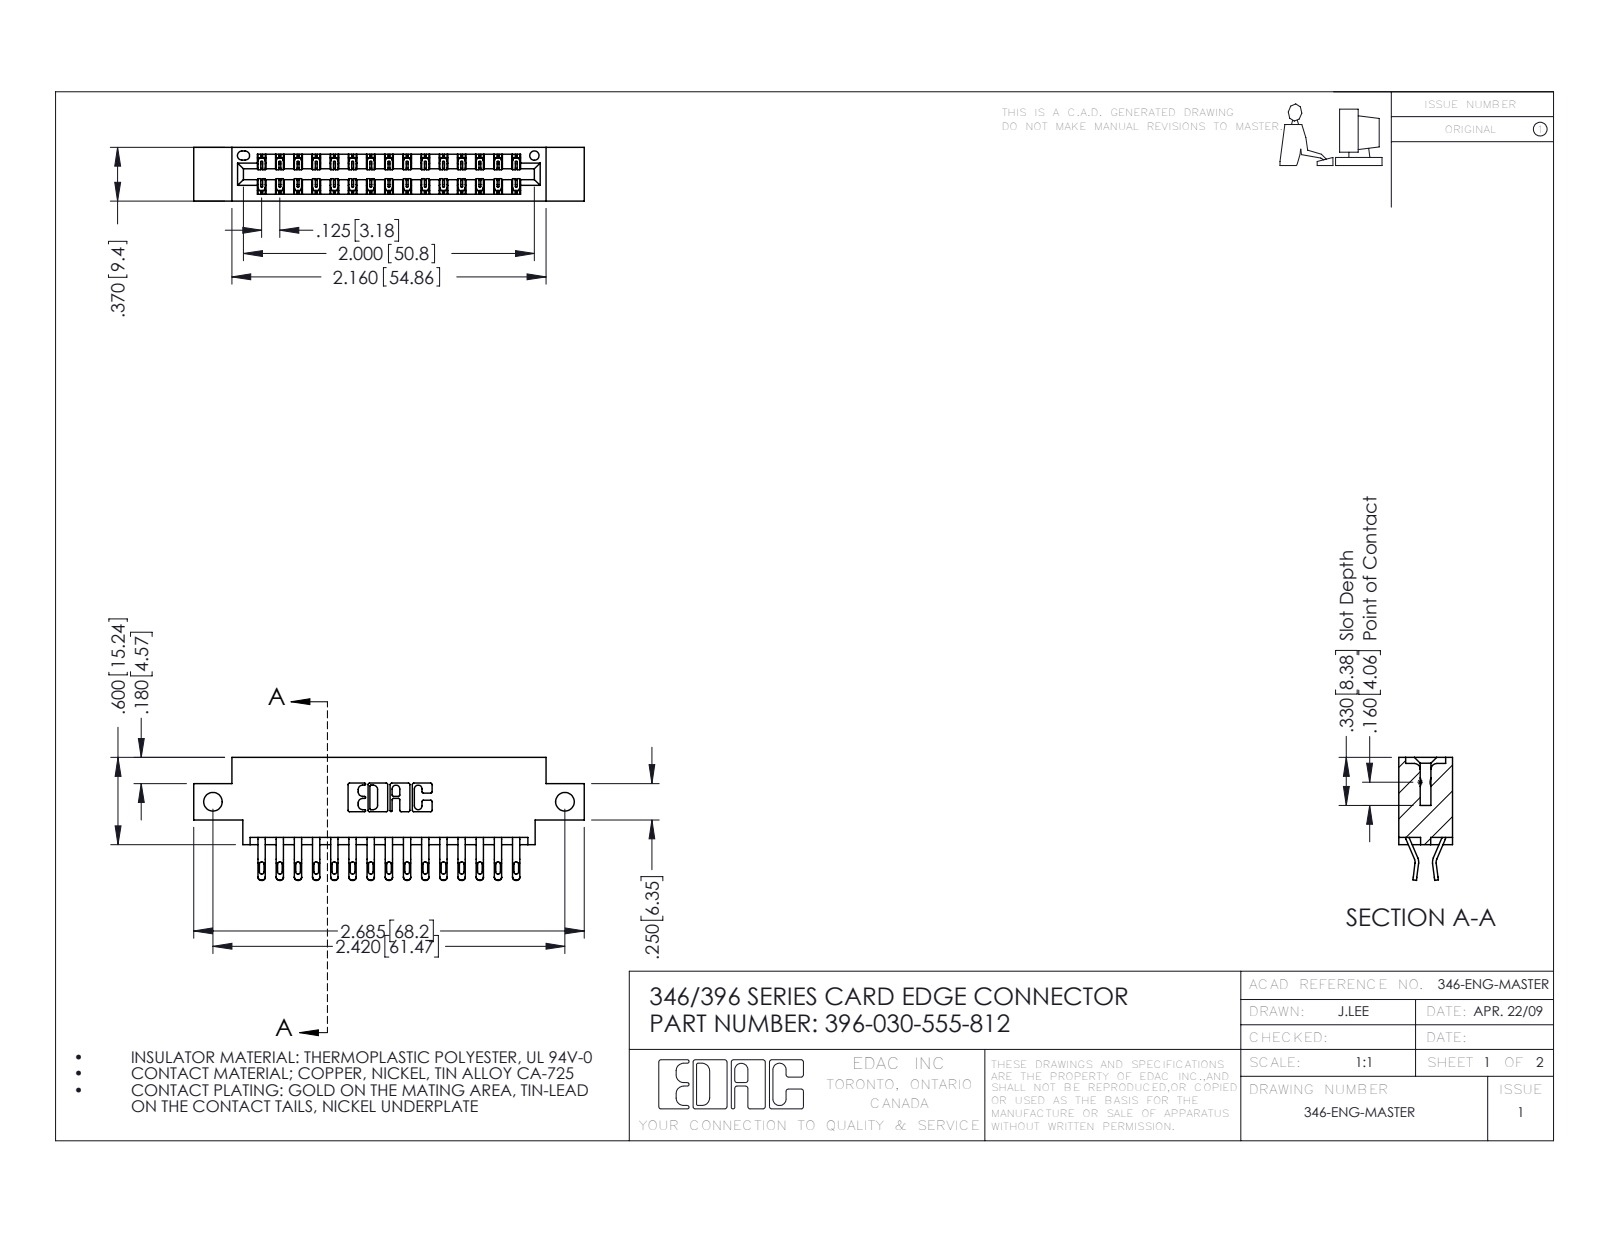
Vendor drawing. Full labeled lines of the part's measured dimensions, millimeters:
Part name (STEP PRODUCT): 346 Part_0.170 Offset - Side Mount; 396-030-555-812; 345-292-001_555 Tail
STEP written by: SolidWorks 2016 (CONFIG_CONTROL_DESIGN)
Units: millimetres
Bodies: 31 solids, 1866 faces (1070 planar, 796 cylindrical, 0 other)
Overall size (bounding box): 68.2 × 21.5 × 9.4
Volume: 6 290 mm³ · Surface area: 8 568 mm²
Round holes (diameter × count): ⌀3.3 ×2, ⌀1.6 ×1
Partial cylindrical surfaces — rounded edges, fillets, slot ends (radius × count): R0.4 ×60, R0.5 ×60, R0.2 ×45, R0.3 ×22, R0.2 ×6, R0.8 ×6, R0.7 ×3, R0.3 ×2
Main face-to-face distances: 1.2, 8.2, 9.4, 6.4, 0.6, 1.8, 7.6, 7, 3.8, 5.6
Hole centre spacings: 61.5
